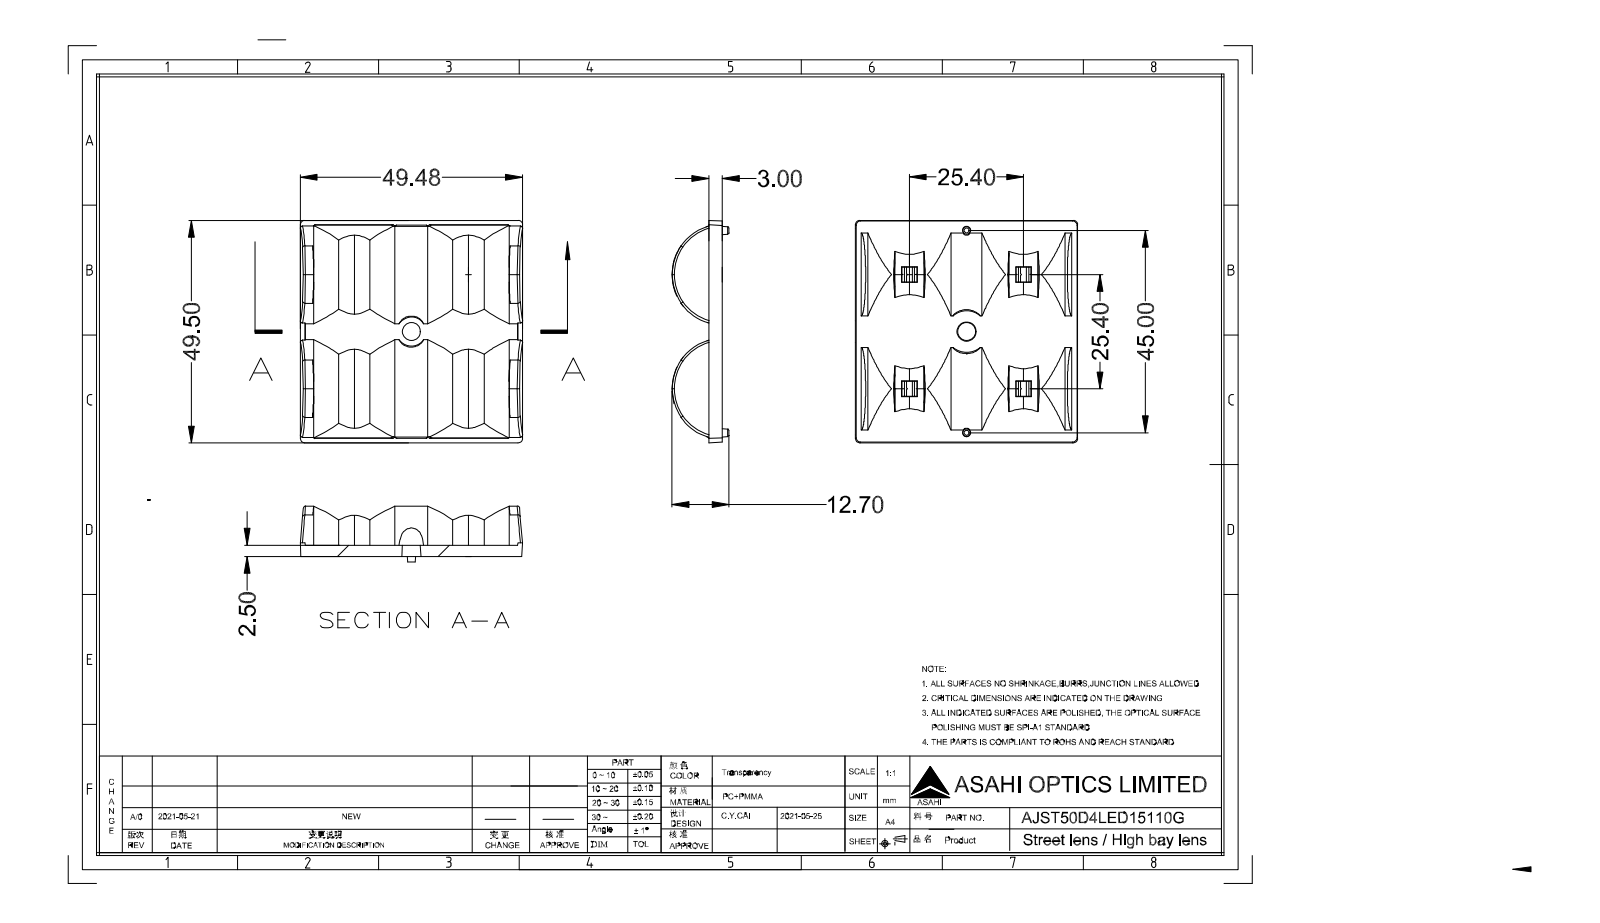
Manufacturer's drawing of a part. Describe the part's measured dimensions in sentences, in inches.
The part is named "AdmiB0685A81pm94". Its 3-D file was written by "SIEMENS PLM Software NX 10.0 (AUTOMOTIVE_DESIGN)". It is 5 solids with 306 faces: 170 planar, 43 cylindrical and 93 other. Overall it measures 1.949 by 1.948 by 0.5 inches. Its volume is 0.694 cubic inches and its surface area 14.34 square inches. Partial cylindrical surfaces (rounded edges, fillets, slot ends): 4 of radius 0.01, 4 of radius 0.039, 2 of radius 0.362, 2 of radius 0.441, 1 of radius 0.012, 1 of radius 0.014. The main face-to-face distances are 0.098, 1, 0.205, 0.106, 0.276, 0.404, 0.02, 0.118, 0.087, 1.276. The hole center spacings are 1, 0.118, 1.007, 1.414, 0.882, 1.118, 1.333, 1.5.
